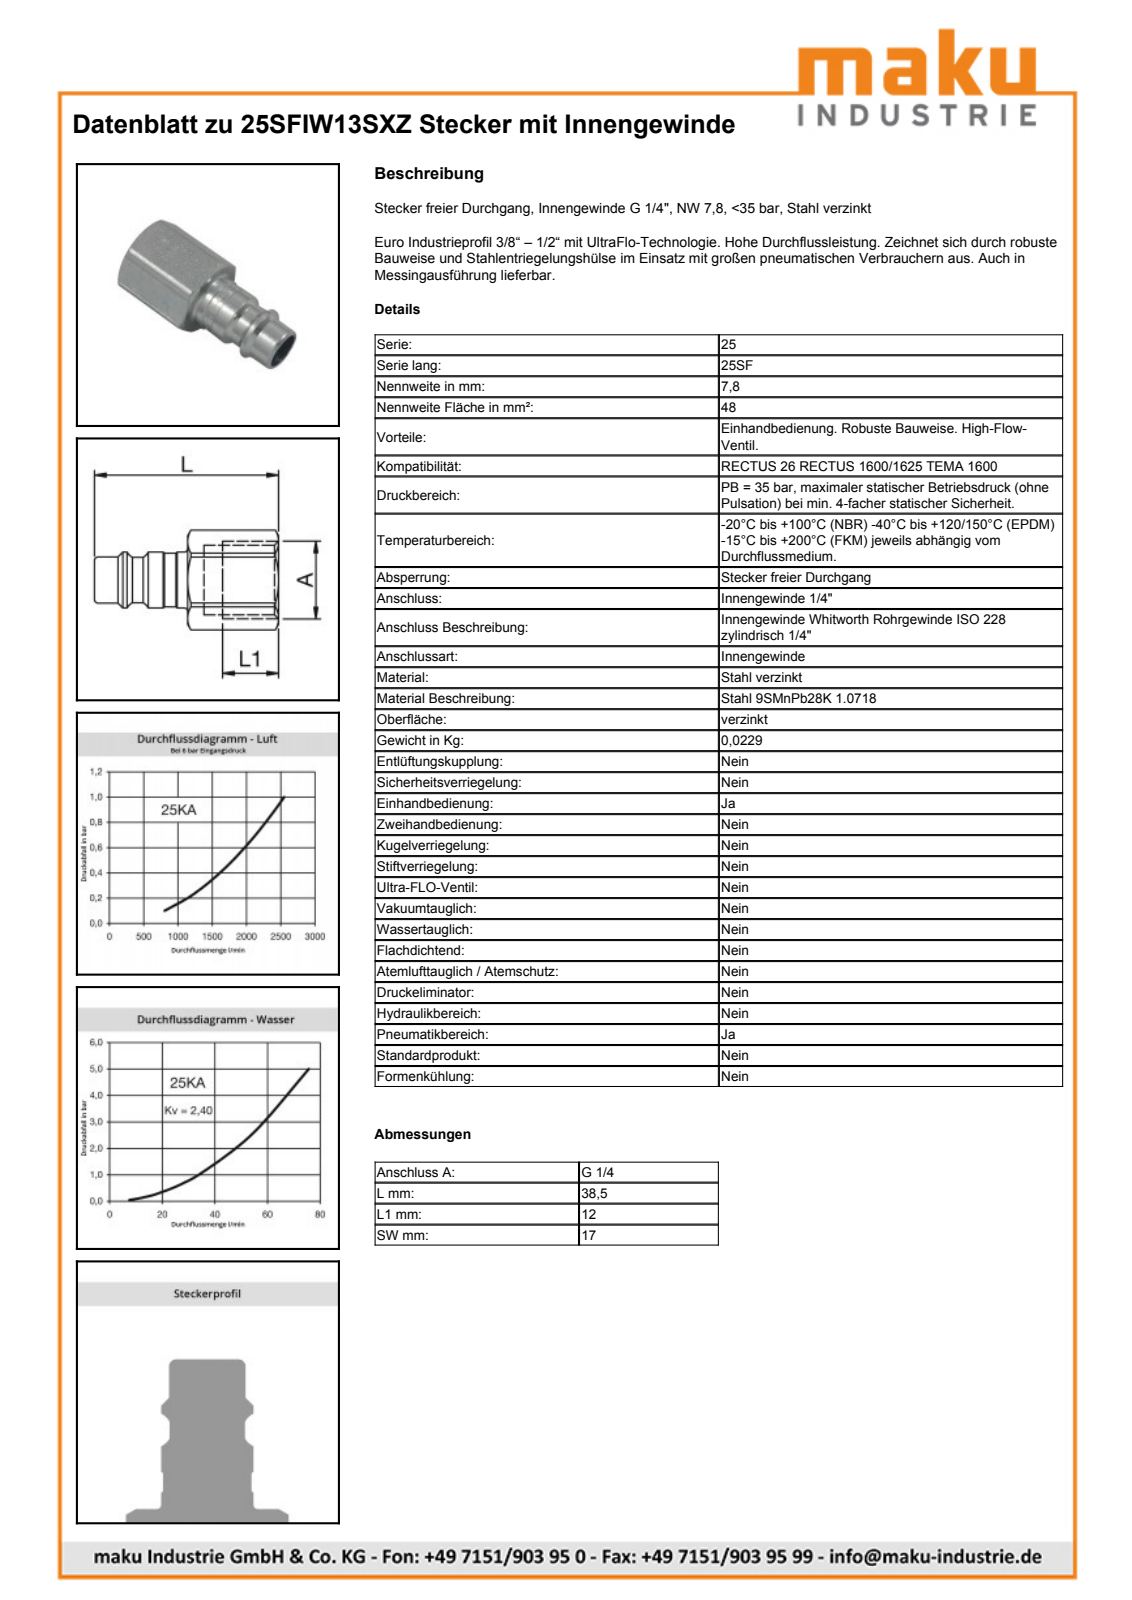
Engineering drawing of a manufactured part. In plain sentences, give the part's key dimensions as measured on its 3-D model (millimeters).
The part is named "D102455". Its 3-D file was written by "Autodesk Inventor 2013 (AUTOMOTIVE_DESIGN)". It is 1 solid with 41 faces: 9 planar, 12 cylindrical and 20 other. Overall it measures 38.5 by 19.15 by 17 millimeters. Its volume is 3 751 cubic millimeters and its surface area 3 229 square millimeters. Round holes: 1 of diameter 7.85, 1 of diameter 11.45. Round bosses or shafts: 1 of diameter 12, 1 of diameter 9.9, 1 of diameter 9.75. Partial cylindrical surfaces (rounded edges, fillets, slot ends): 1 of radius 9.57. The main face-to-face distances are 17, 18.5, 38.5, 20.
